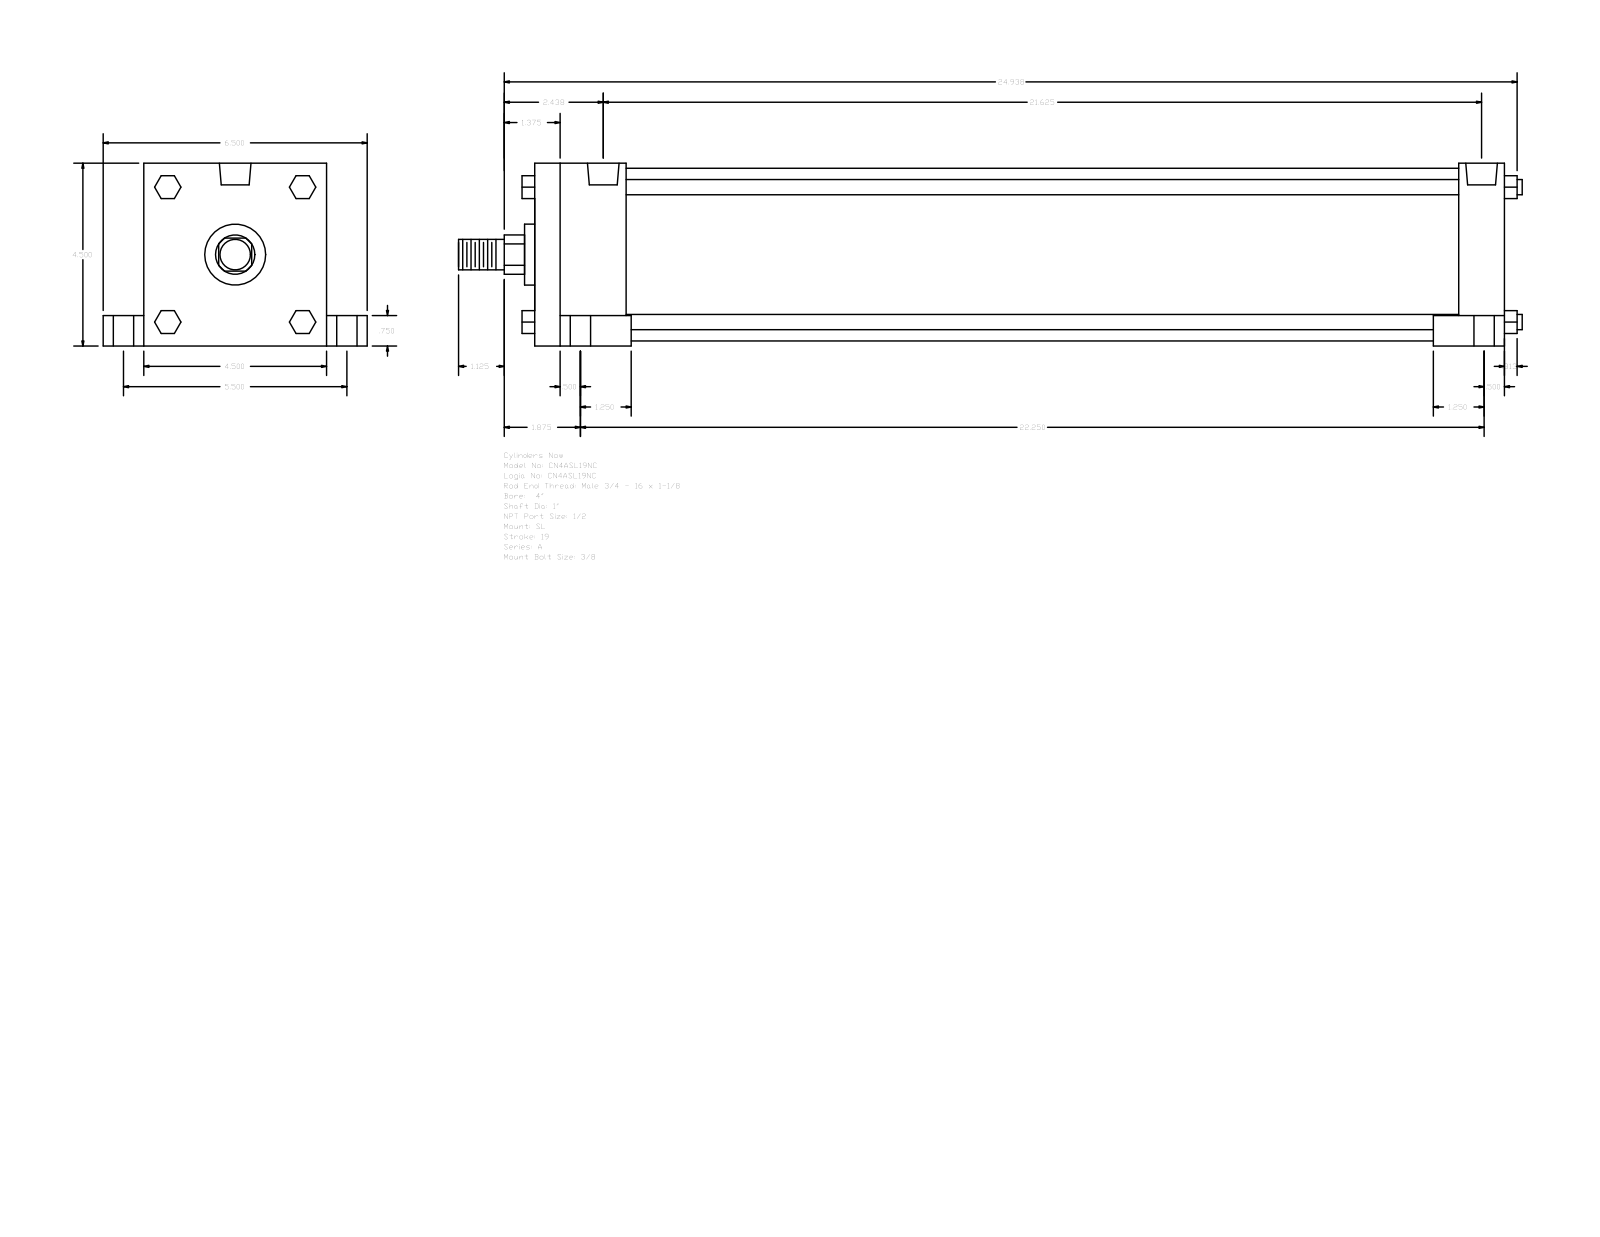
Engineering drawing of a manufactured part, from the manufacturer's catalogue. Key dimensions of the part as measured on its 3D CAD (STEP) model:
Part name (STEP PRODUCT): A_SL__0400_1
STEP written by: GSSL Pune (CONFIG_CONTROL_DESIGN)
Units: millimetres
Bodies: 0 solids, 150 faces (114 planar, 36 cylindrical, 0 other)
Overall size (bounding box): 665.16 × 165.1 × 114.3
Round holes (diameter × count): ⌀8.73 ×4, ⌀12.7 ×4, ⌀19.05 ×4, ⌀19.77 ×2
Round bosses / shafts (diameter × count): ⌀9.53 ×4, ⌀107.95 ×1, ⌀38.1 ×1, ⌀25.4 ×1, ⌀19.05 ×1
Partial cylindrical surfaces — rounded edges, fillets, slot ends (radius × count): R12.29 ×1
Main face-to-face distances: 114.3, 606.43, 57.15, 549.28, 577.85, 520.7, 28.58, 19.05, 25.4, 139.7
Hole centre spacings: 3.18, 69.87, 70.01, 71.3, 72, 139.7, 542.92, 546.1
